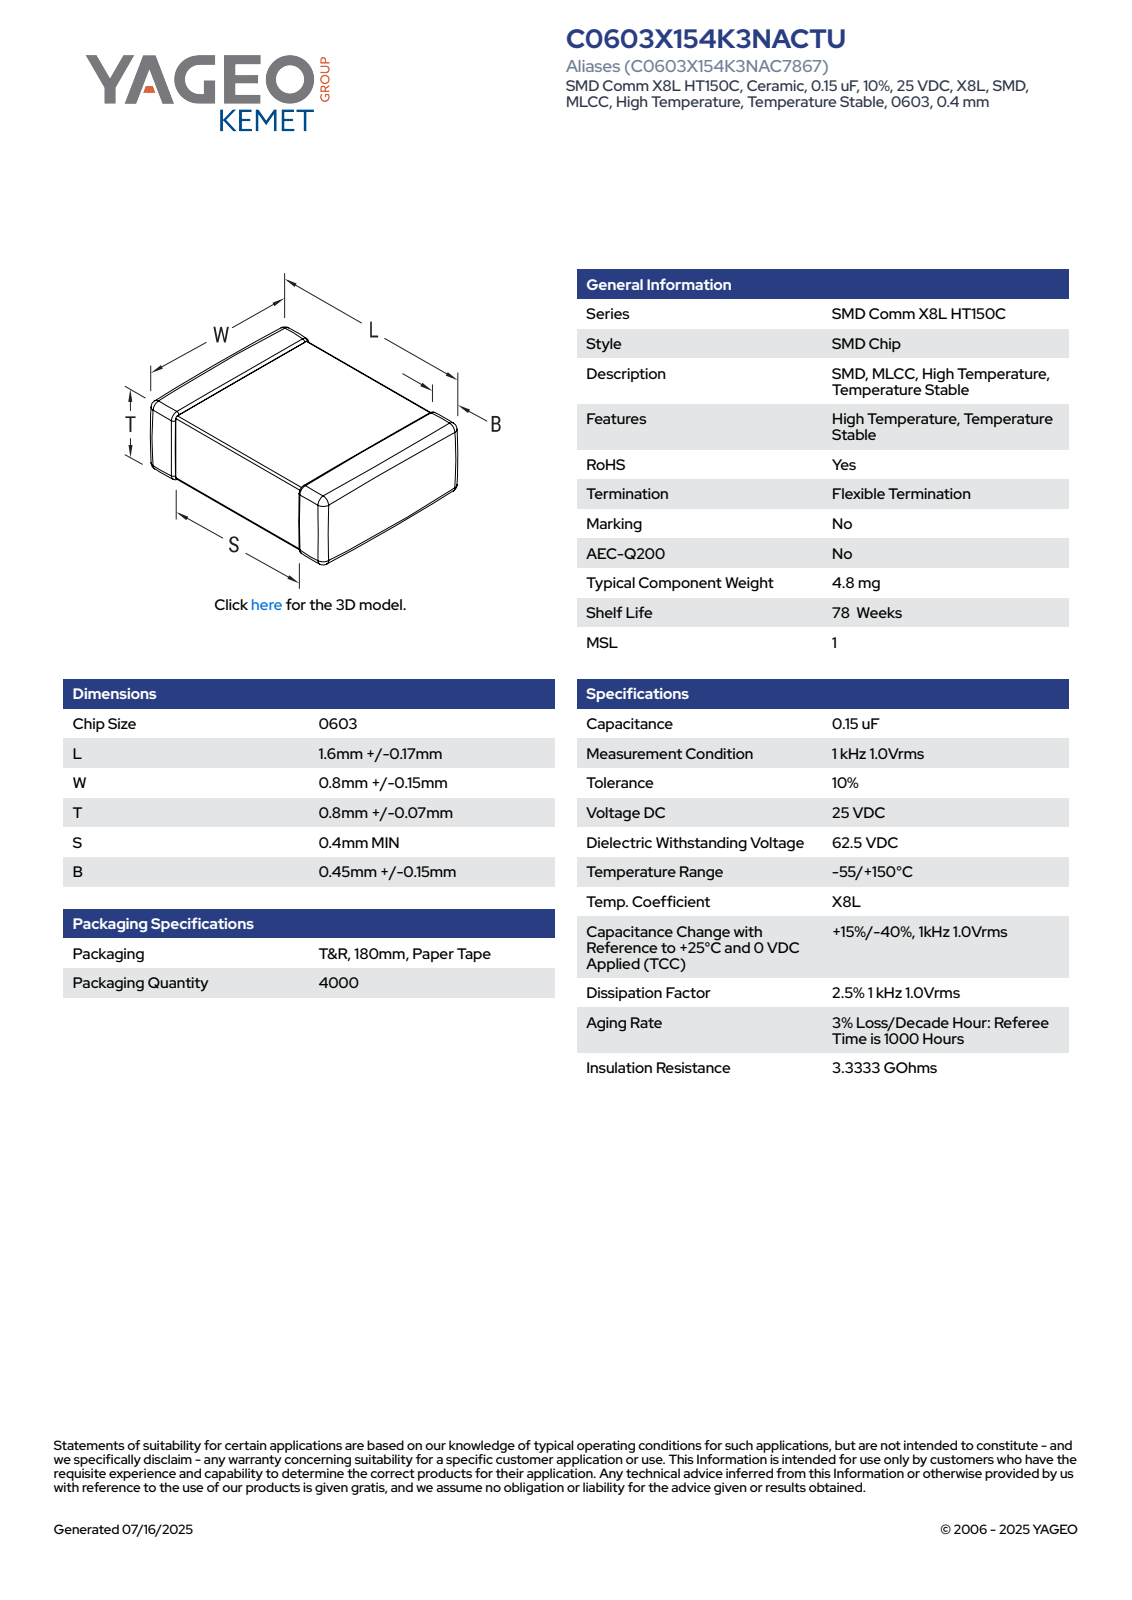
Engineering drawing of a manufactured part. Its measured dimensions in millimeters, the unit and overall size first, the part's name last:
Units: millimetres
Overall size (bounding box): 1.77 × 0.95 × 0.87
Main face-to-face distances: 0.85, 0.87, 0.95, 0.93, 1.77, 0.83, 0.91, 0.84, 0.86, 0.82
Volume: 1 mm³ · Surface area: 8 mm²
Bodies: 4 solids, 125 faces (71 planar, 38 cylindrical, 16 other)
Part name (STEP PRODUCT): CCS_CCSTD_0603_L1.77W0.95S0.8T0.87B0.45
STEP written by: SolidWorks 2021 (AUTOMOTIVE_DESIGN)
